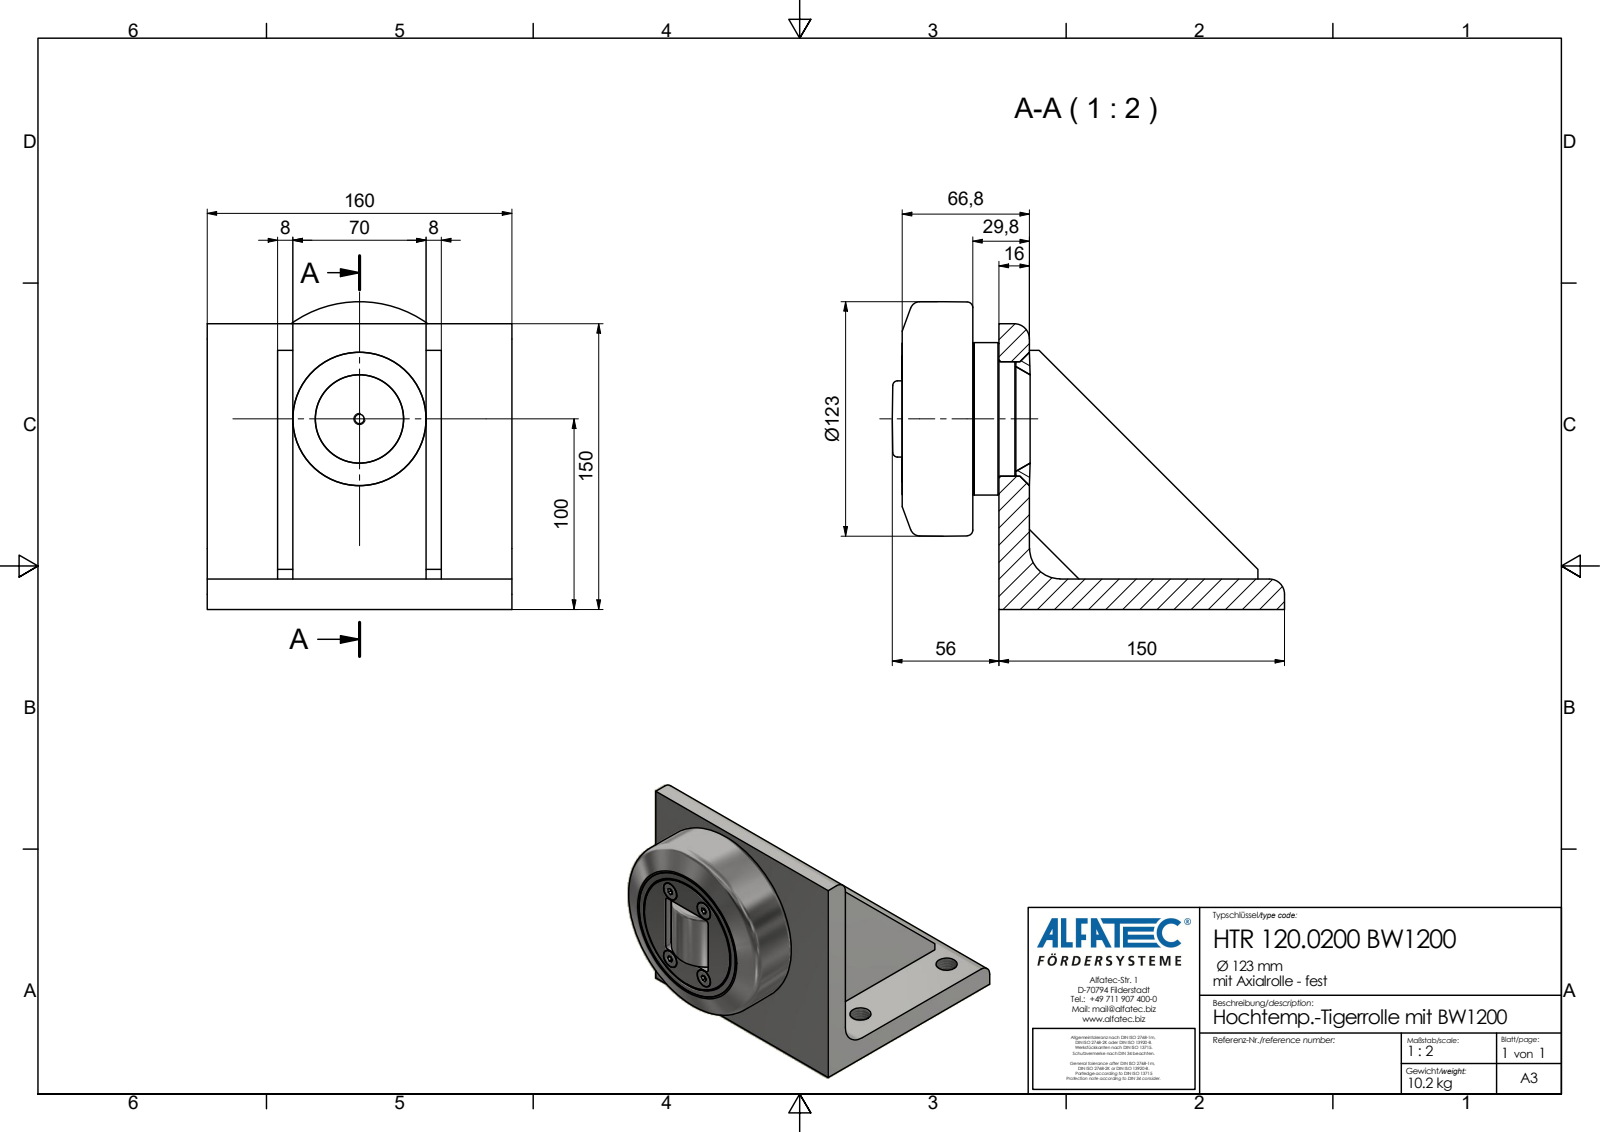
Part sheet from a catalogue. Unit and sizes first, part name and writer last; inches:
Units: inches
Overall size (bounding box): 8.11 × 6.358 × 6.299
Round holes (diameter × count): ⌀0.545 ×4, ⌀0.194 ×1
Round bosses / shafts (diameter × count): ⌀0.472 ×4, ⌀3.15 ×1
Partial cylindrical surfaces — rounded edges, fillets, slot ends (radius × count): R0.315 ×2, R0.63 ×1
Main face-to-face distances: 0.63, 0.315, 3.071, 1.457, 1.772, 4.528, 4.843, 2.756, 3.386, 1.173
Hole centre spacings: 3.15, 4.724, 5.678
Volume: 81.65 in³ · Surface area: 254.3 in²
Bodies: 1 solid, 89 faces (60 planar, 14 cylindrical, 15 other)
Part name (STEP PRODUCT): HTR 120.0200 BW1200_Kontur
STEP written by: Autodesk Inventor 2020 (AP242_MANAGED_MODEL_BASED_3D_ENGINEERING_MIM_LF)
